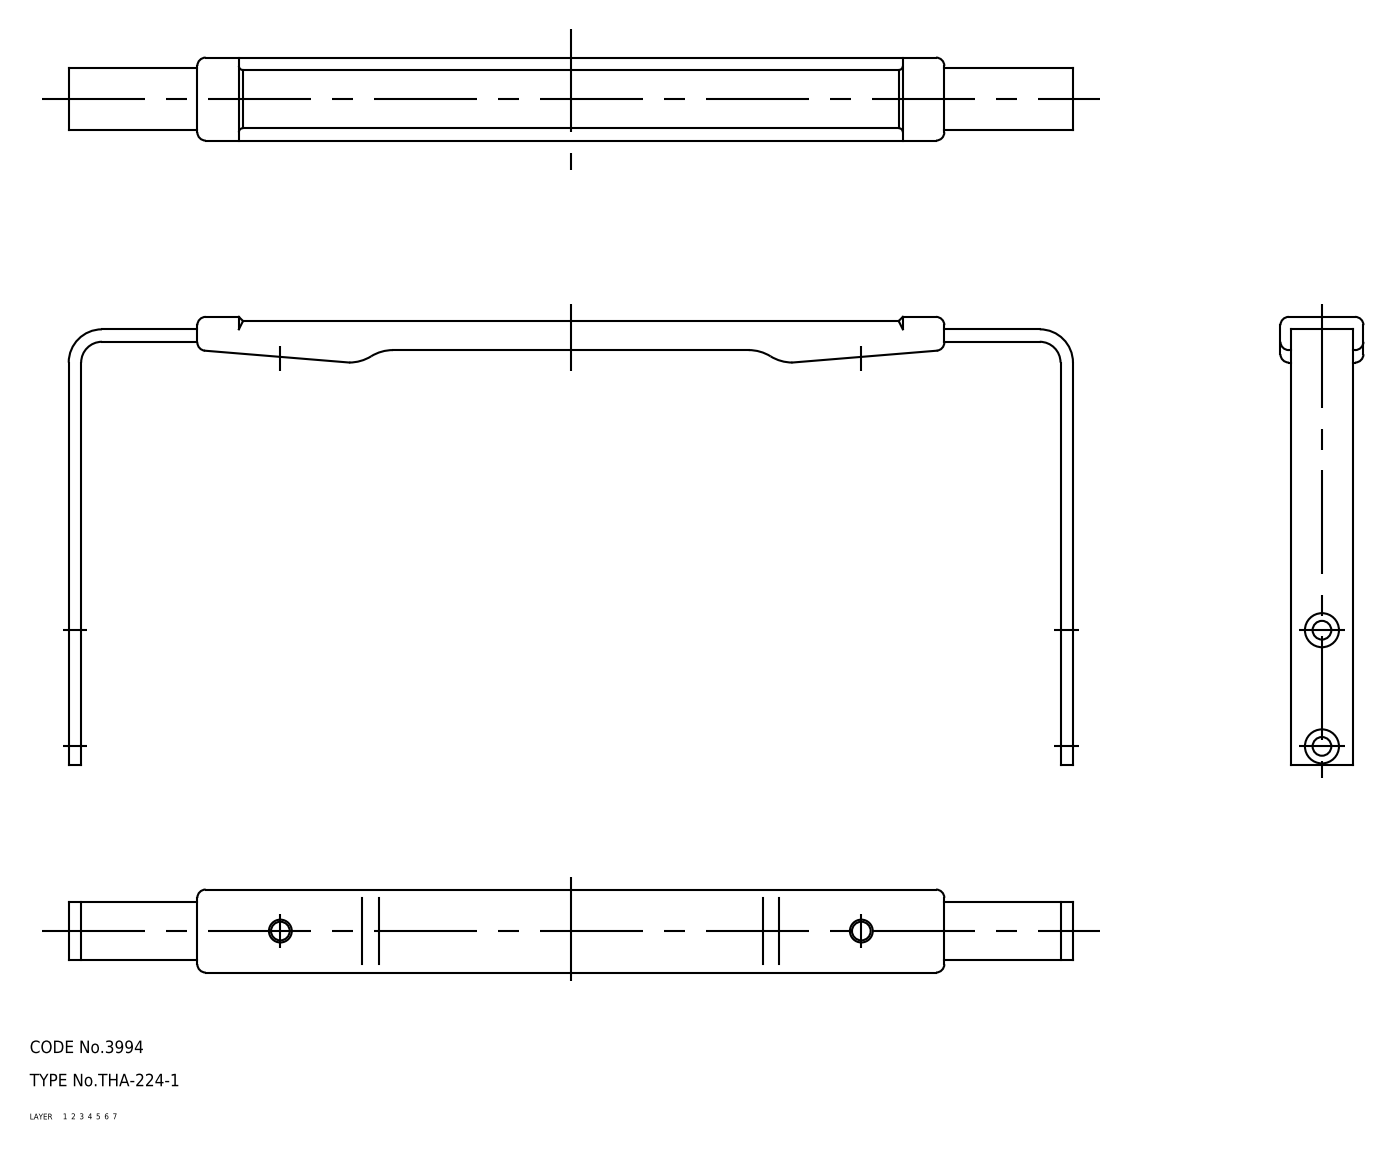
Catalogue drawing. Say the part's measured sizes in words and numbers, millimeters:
The part is named "pull; grip; THA_224_1_24371_36". Its 3-D file was written by "CADfix (AUTOMOTIVE_DESIGN)". It is 2 solids with 98 faces: 0 planar, 0 cylindrical and 98 other. Overall it measures 242 by 108 by 20 millimeters. Its volume is 37 808 cubic millimeters and its surface area 32 250 square millimeters.
